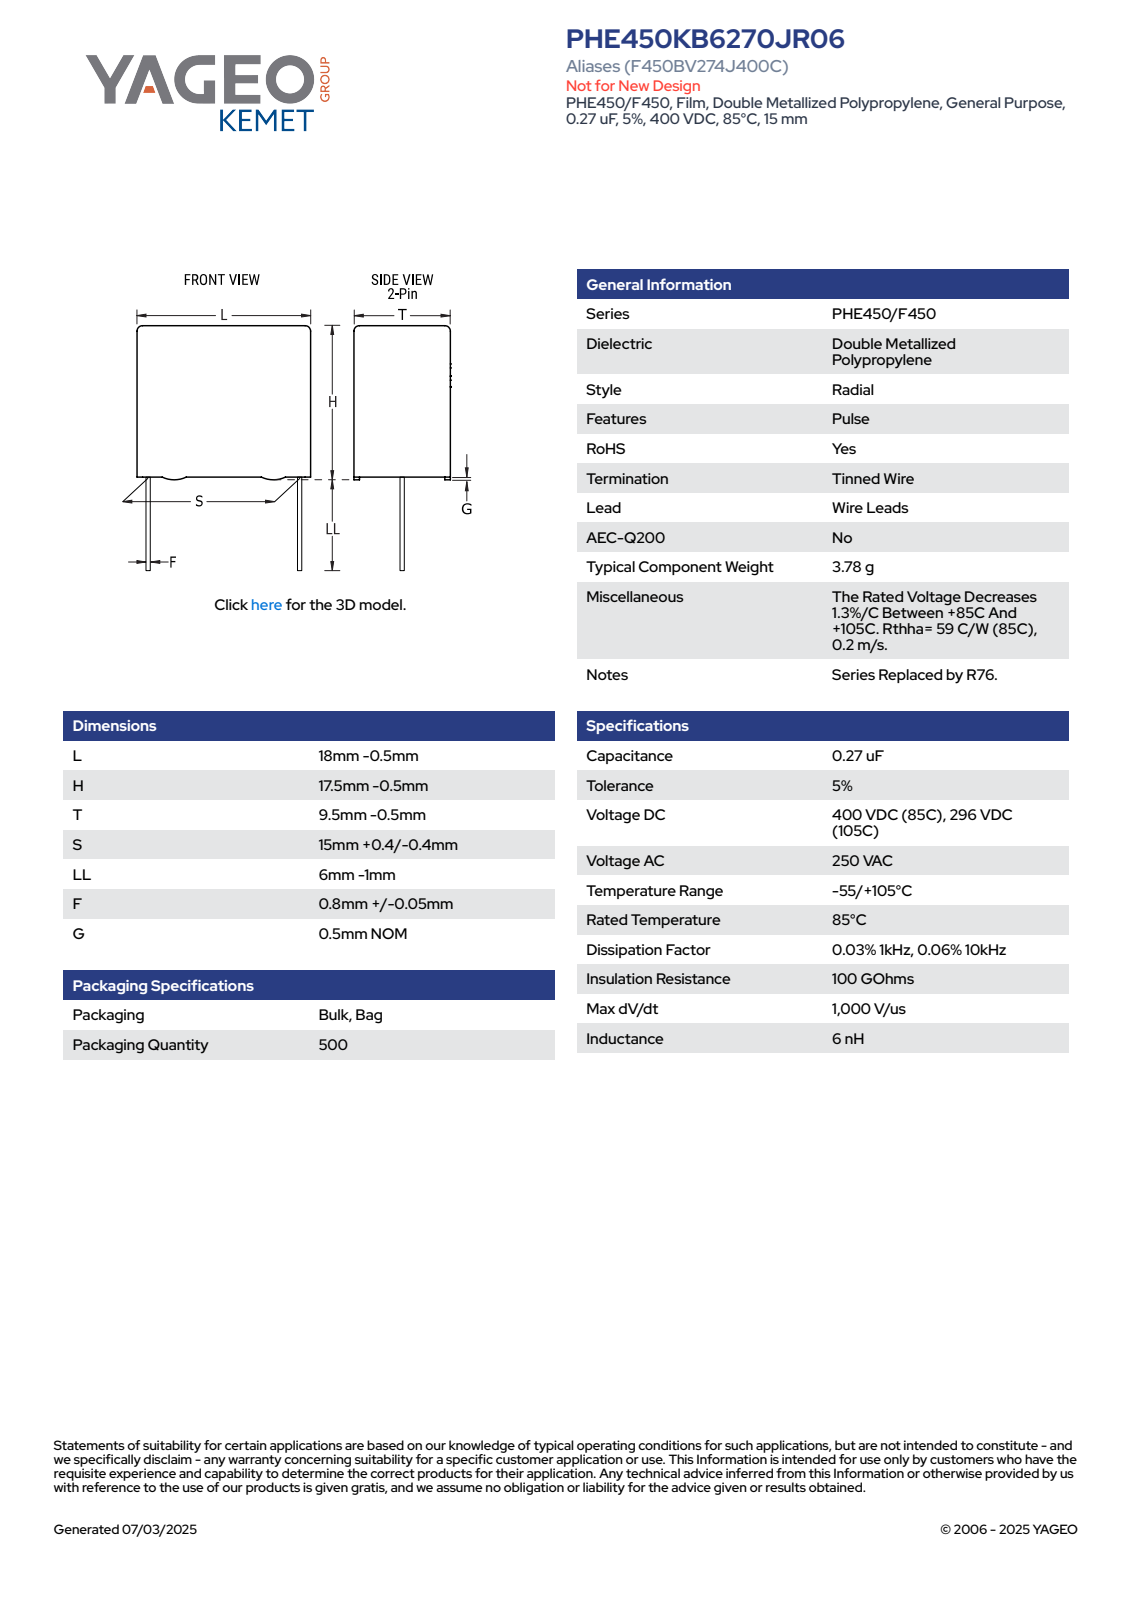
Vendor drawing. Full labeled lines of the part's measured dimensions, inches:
Part name (STEP PRODUCT): CFR_RBG_18X17.5X9.5_L17.5H17T9S15LL5F0.85G0.5
STEP written by: SolidWorks 2020 (AUTOMOTIVE_DESIGN)
Units: inches
Bodies: 4 solids, 89 faces (81 planar, 8 cylindrical, 0 other)
Overall size (bounding box): 0.866 × 0.689 × 0.355
Volume: 0.159 in³ · Surface area: 1.942 in²
Round bosses / shafts (diameter × count): ⌀0.033 ×2
Partial cylindrical surfaces — rounded edges, fillets, slot ends (radius × count): R0.02 ×4
Main face-to-face distances: 0.354, 0.689, 0.65, 0.02, 0.334, 0.02, 0.669, 0.314, 0.197, 0.217
